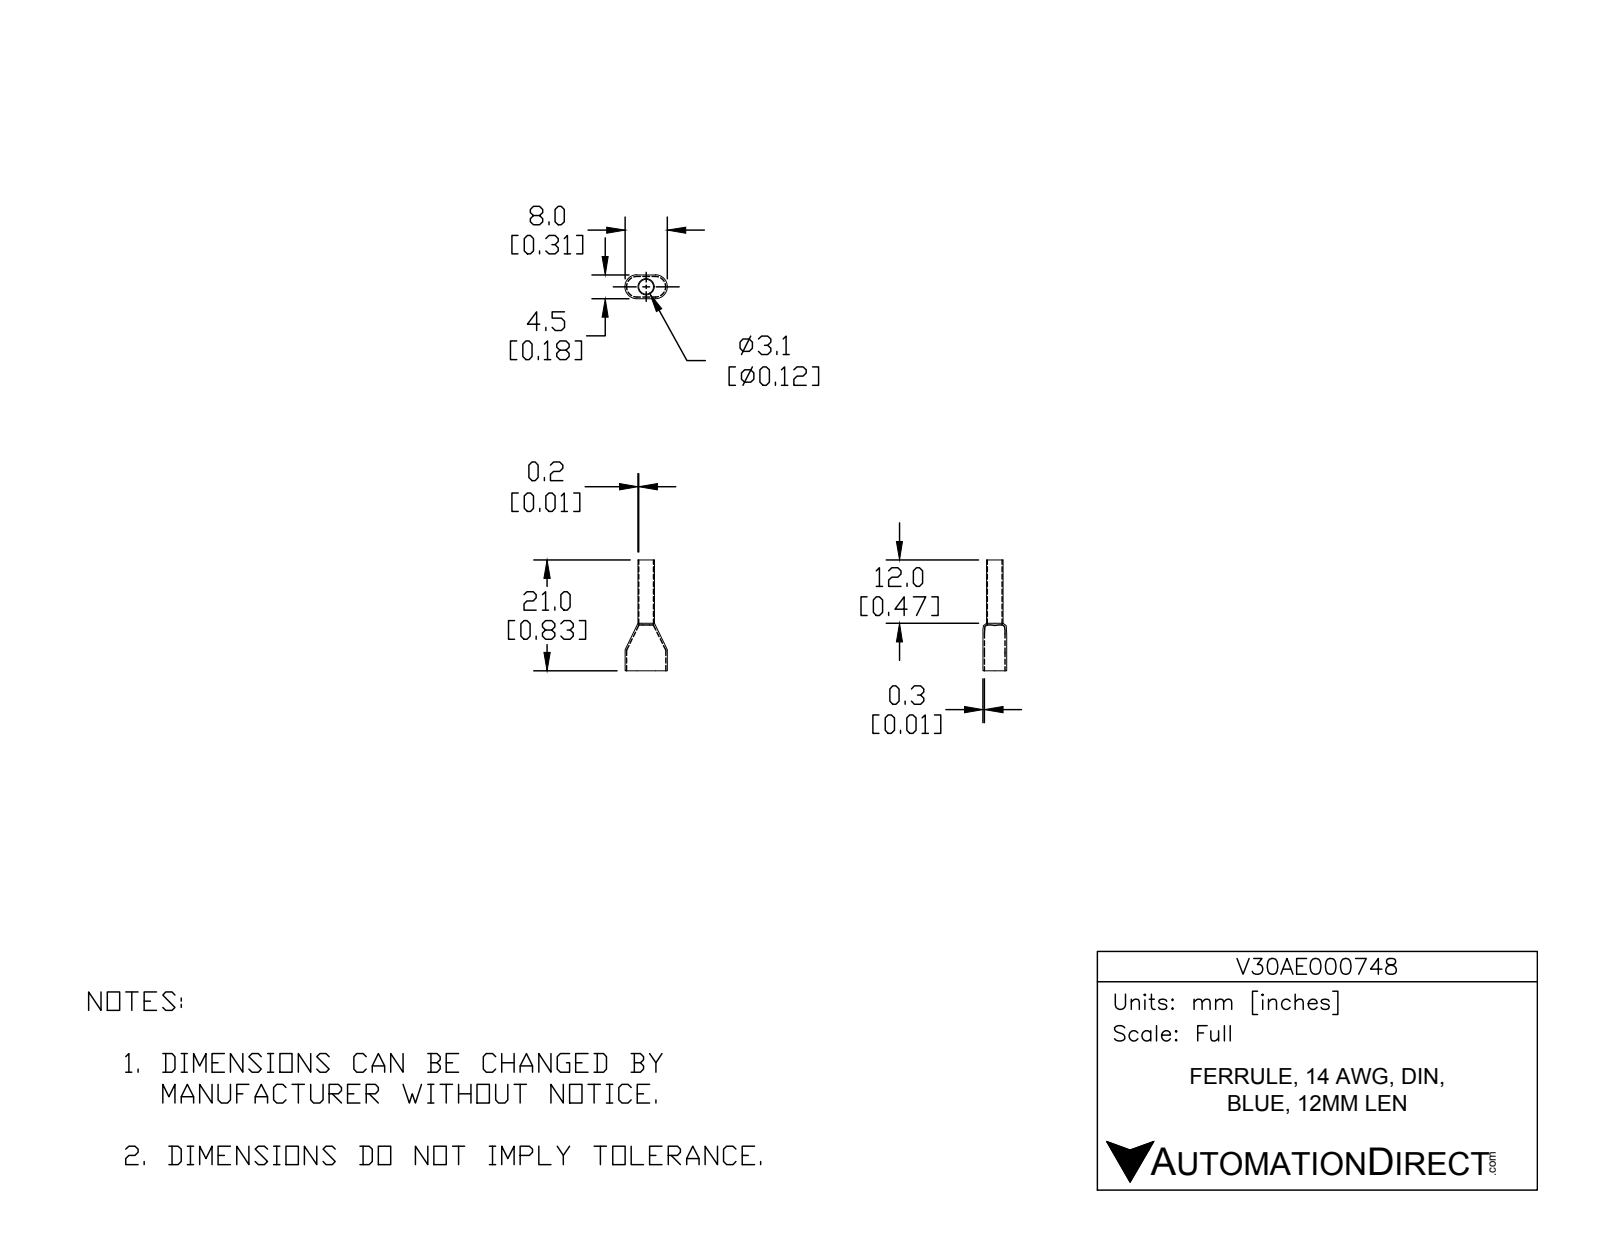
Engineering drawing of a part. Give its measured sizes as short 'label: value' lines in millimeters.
name: V30AE000748
written by: SolidWorks 2017 (AUTOMOTIVE_DESIGN)
unit: mm
bodies: 2 solids, 36 faces (14 planar, 22 cylindrical, 0 other)
size: 21 × 8 × 4.5
volume: 65 mm³; area: 554 mm²
holes: 1× ⌀2.8
bosses: 1× ⌀3.1
rounds: 4× R1.95, 4× R2.25
face distances: 4.2, 4.5, 3.9, 9, 21, 12, 8.7, 12.3
